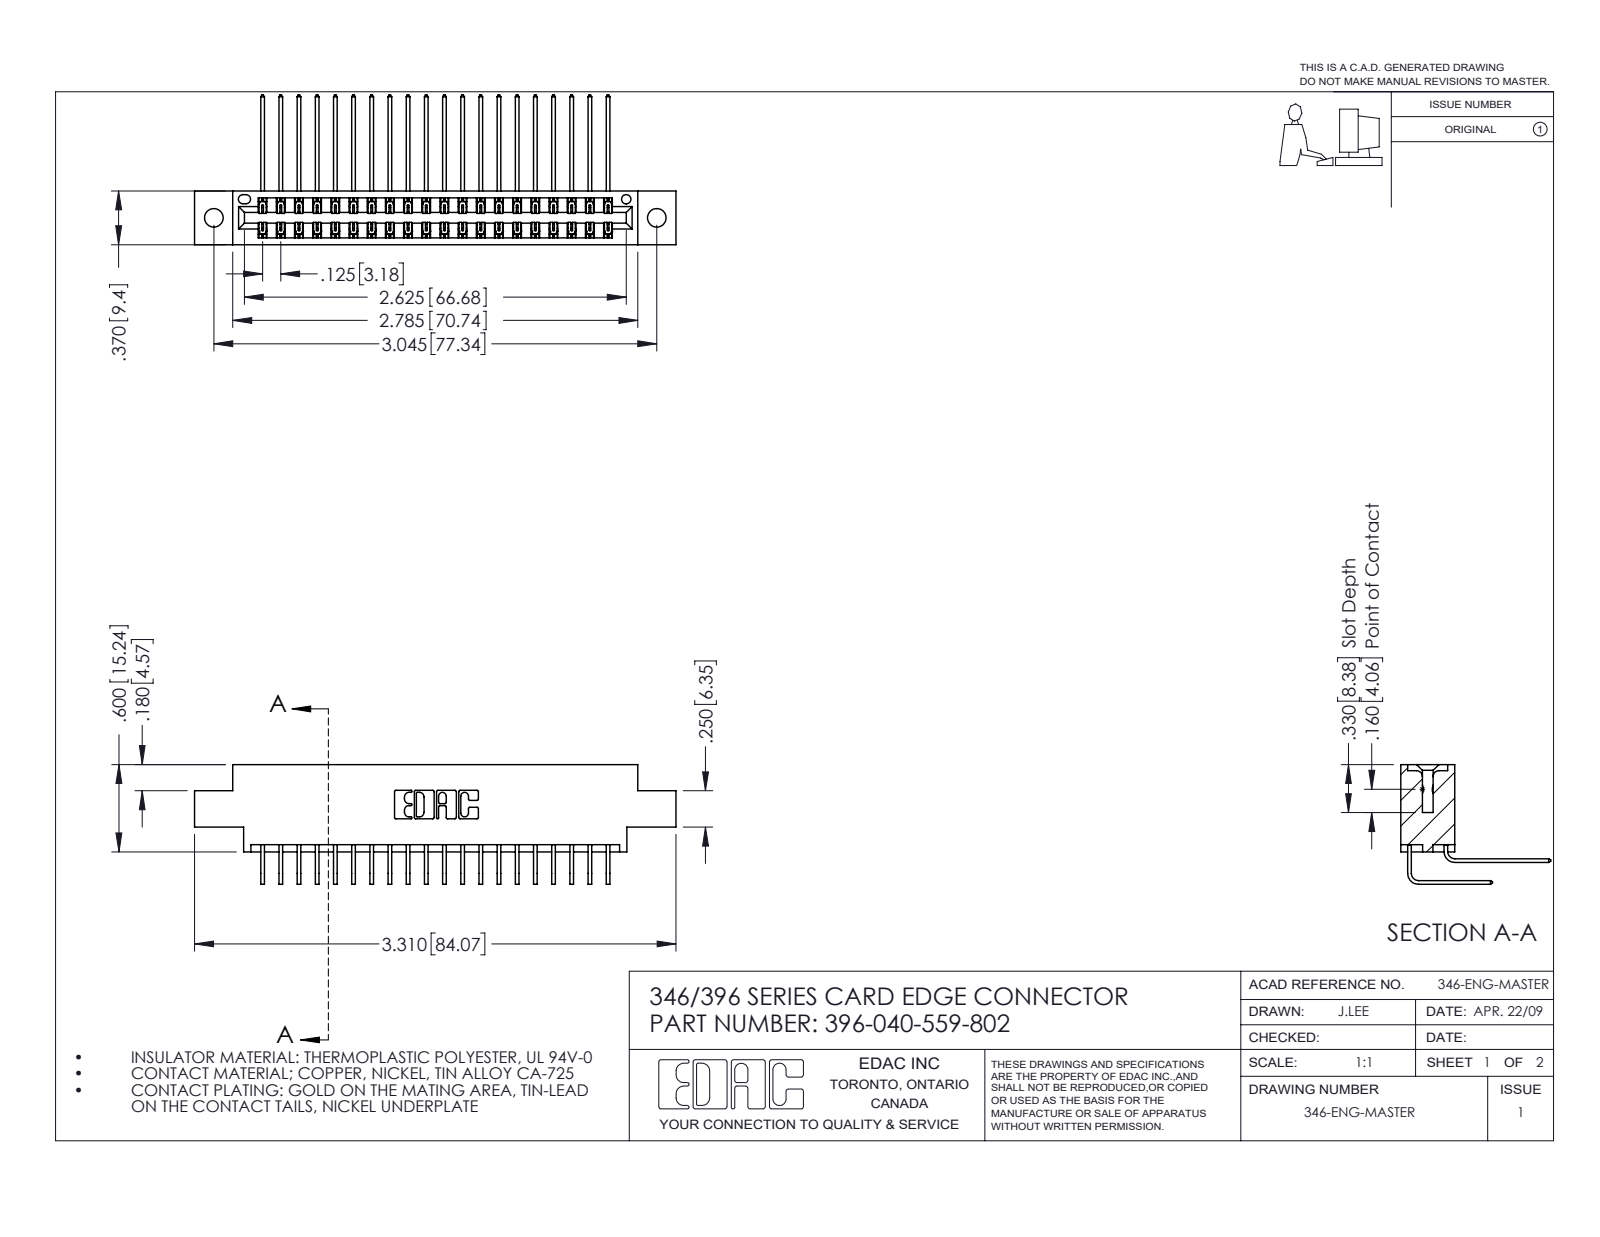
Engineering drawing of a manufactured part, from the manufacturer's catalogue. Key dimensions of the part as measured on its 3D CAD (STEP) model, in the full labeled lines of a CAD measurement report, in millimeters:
Part name (STEP PRODUCT): 346 Part_0.170 Offset - 0.128 Dia; 345-292-001_559 Tail - 2; 396-040-559-802; 345-292-001_558 559 Tail - 1
STEP written by: SolidWorks 2016 (CONFIG_CONTROL_DESIGN)
Units: millimetres
Bodies: 41 solids, 2286 faces (1560 planar, 726 cylindrical, 0 other)
Overall size (bounding box): 84.1 × 26.2 × 20.9
Volume: 8 060 mm³ · Surface area: 11 760 mm²
Round holes (diameter × count): ⌀3.3 ×2, ⌀1.6 ×1
Partial cylindrical surfaces — rounded edges, fillets, slot ends (radius × count): R0.2 ×60, R0.3 ×22, R0.2 ×6, R0.8 ×6, R0.7 ×3, R0.4 ×2, R0.6 ×2, R0.6 ×2
Main face-to-face distances: 1.2, 8.2, 9.4, 0.6, 6.4, 1.8, 7.6, 7, 3.8, 3.8
Hole centre spacings: 6.2, 72.1, 77.3
